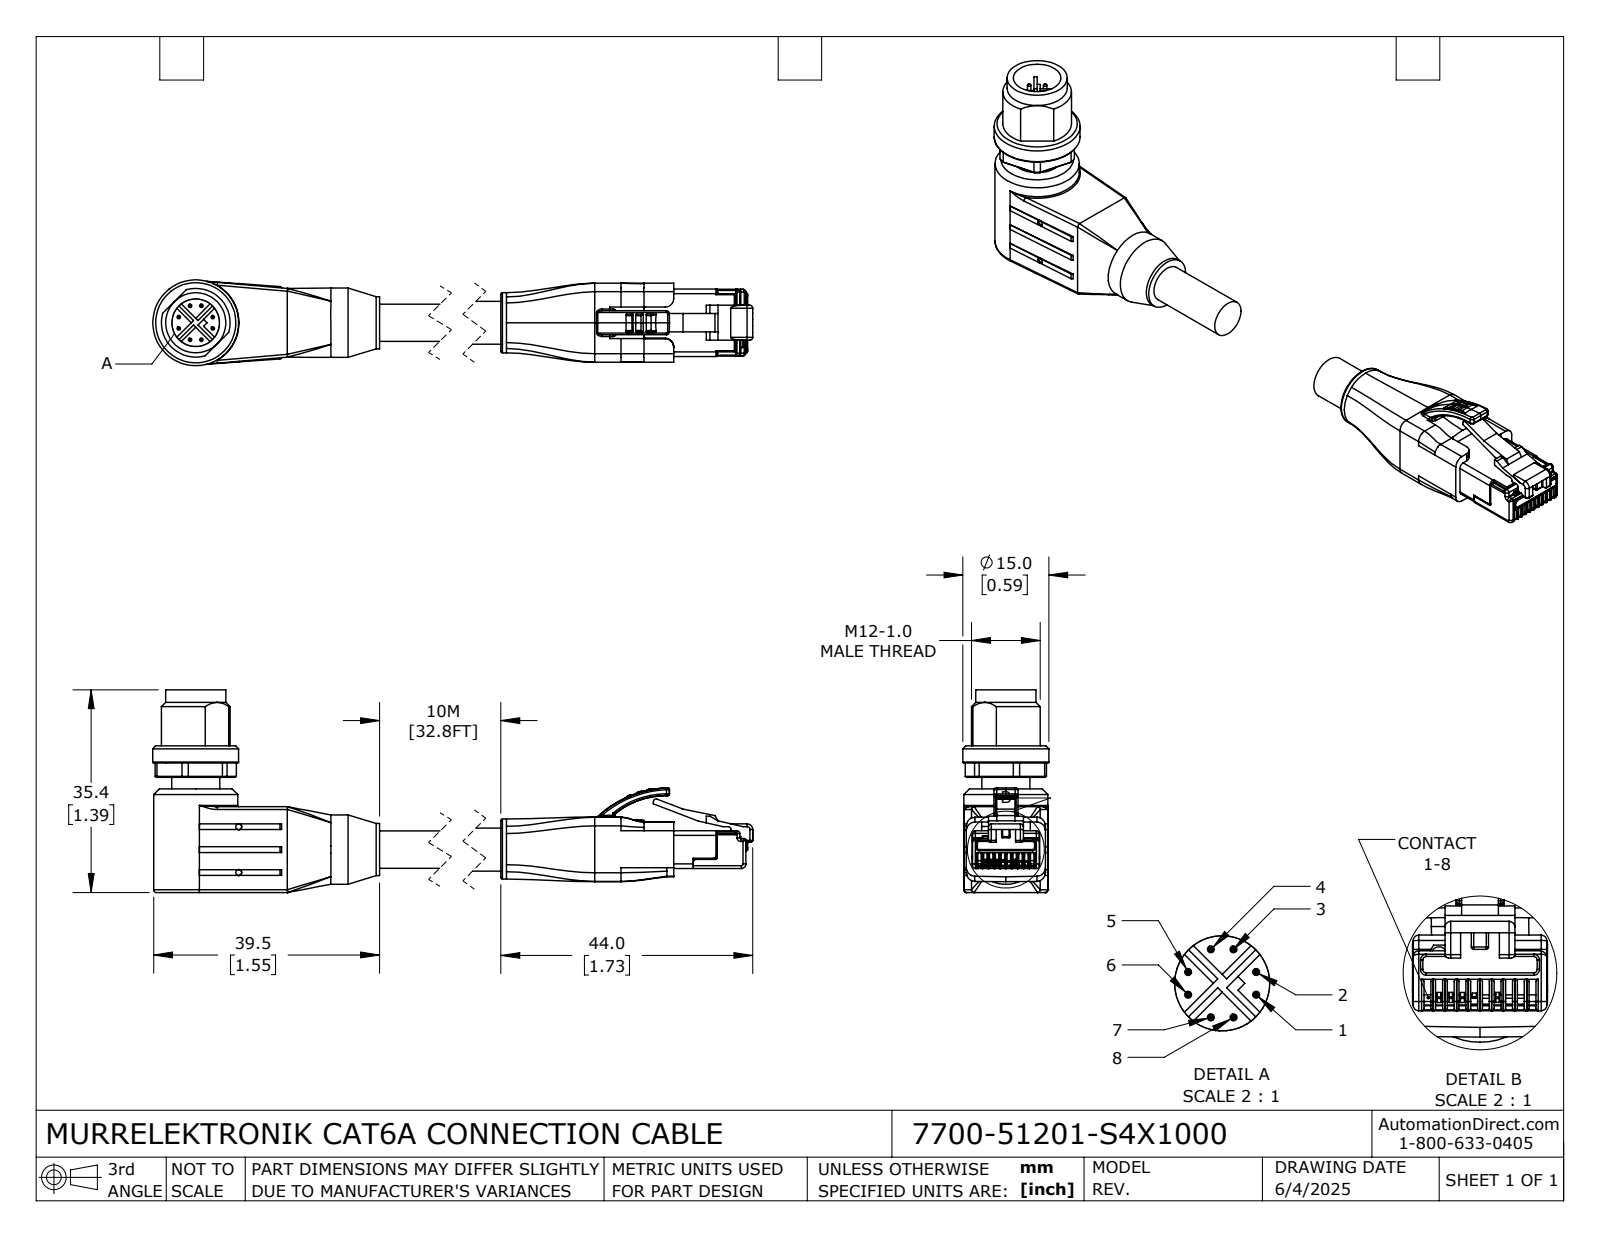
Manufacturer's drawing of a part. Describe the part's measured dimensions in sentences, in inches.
The part is named "7700-51201-S4X1000_MALE; 7700-51201-S4X1000; 7700-51201-S4X1000_RJ45". Its 3-D file was written by "SolidWorks 2024 (CONFIG_CONTROL_DESIGN)". It is 2 solids with 822 faces: 394 planar, 249 cylindrical and 179 other. Overall it measures 5.181 by 1.394 by 0.591 inches. Its volume is 0.874 cubic inches and its surface area 10.17 square inches. Round holes: 4 of diameter 0.041, 1 of diameter 0.189, 1 of diameter 0.327. Round bosses or shafts: 8 of diameter 0.024, 2 of diameter 0.413, 1 of diameter 0.591, 1 of diameter 0.579, 1 of diameter 0.476, 1 of diameter 0.358, 1 of diameter 0.331, 1 of diameter 0.295. Partial cylindrical surfaces (rounded edges, fillets, slot ends): 61 of radius 0.008, 29 of radius 0.02, 16 of radius 0.012, 9 of radius 0.059, 5 of radius 0.031, 2 of radius 0.021, 2 of radius 0.197, 1 of radius 0.005. The main face-to-face distances are 0.425, 0.165, 0.591, 0.543, 0.201, 0.185, 0.791, 0.366, 0.713, 0.228. The hole center spacings are 0.315.
